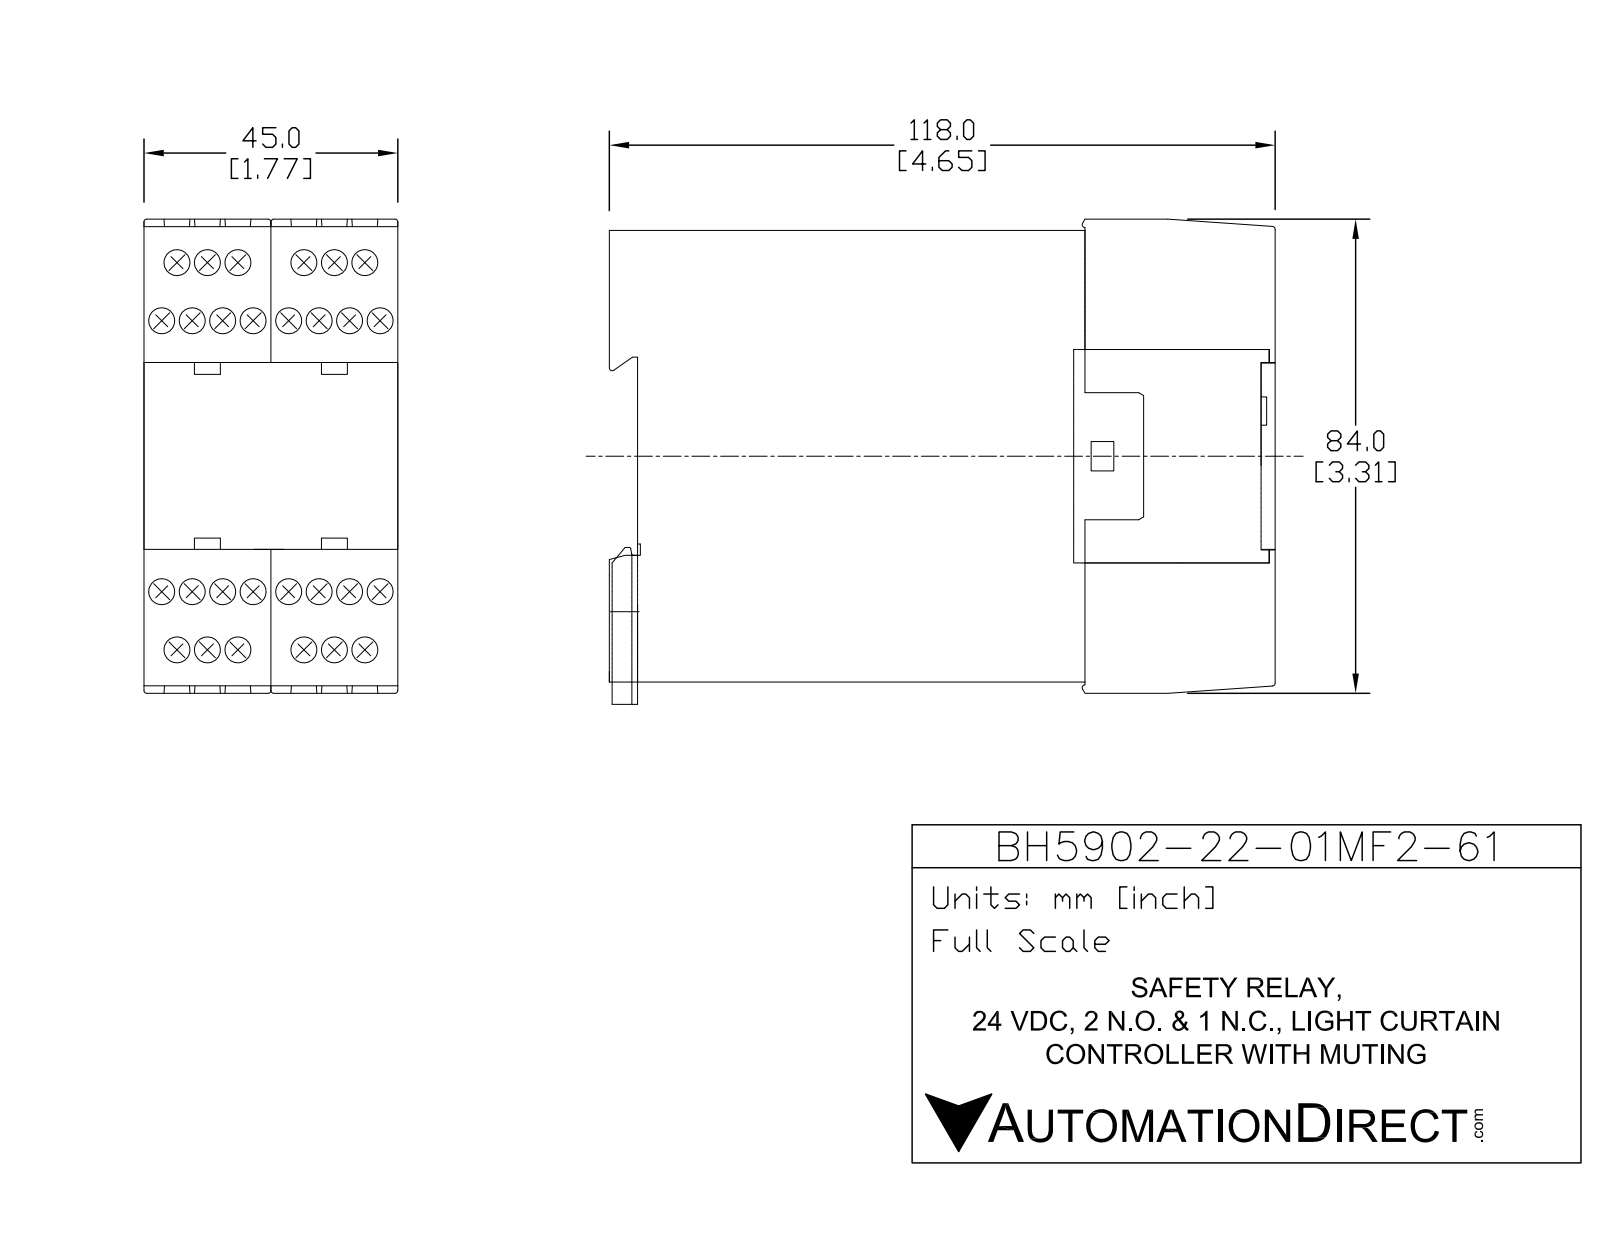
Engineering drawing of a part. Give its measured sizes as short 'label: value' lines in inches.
name: BH5902-22-01MF2-61
written by: SolidWorks 2017 (AUTOMOTIVE_DESIGN)
unit: in
bodies: 1 solid, 1533 faces (1034 planar, 369 cylindrical, 130 other)
size: 4.654 × 3.346 × 1.772
volume: 24.87 in³; area: 74.68 in²
holes: 28× ⌀0.181, 2× ⌀0.315
bosses: 1× ⌀0.087
rounds: 133× R0.02, 64× R0.008, 32× R0.059, 8× R0.049, 3× R0.079, 2× R0.012, 1× R0.043, 1× R0.085
face distances: 1.772, 3.15, 1.77, 4.449, 0.079, 3.071, 1.768, 0.037, 2.992, 0.884
hole spacings: 0.419, 2.306, 0.213, 0.516, 2.325, 0.886, 0.425, 0.879
